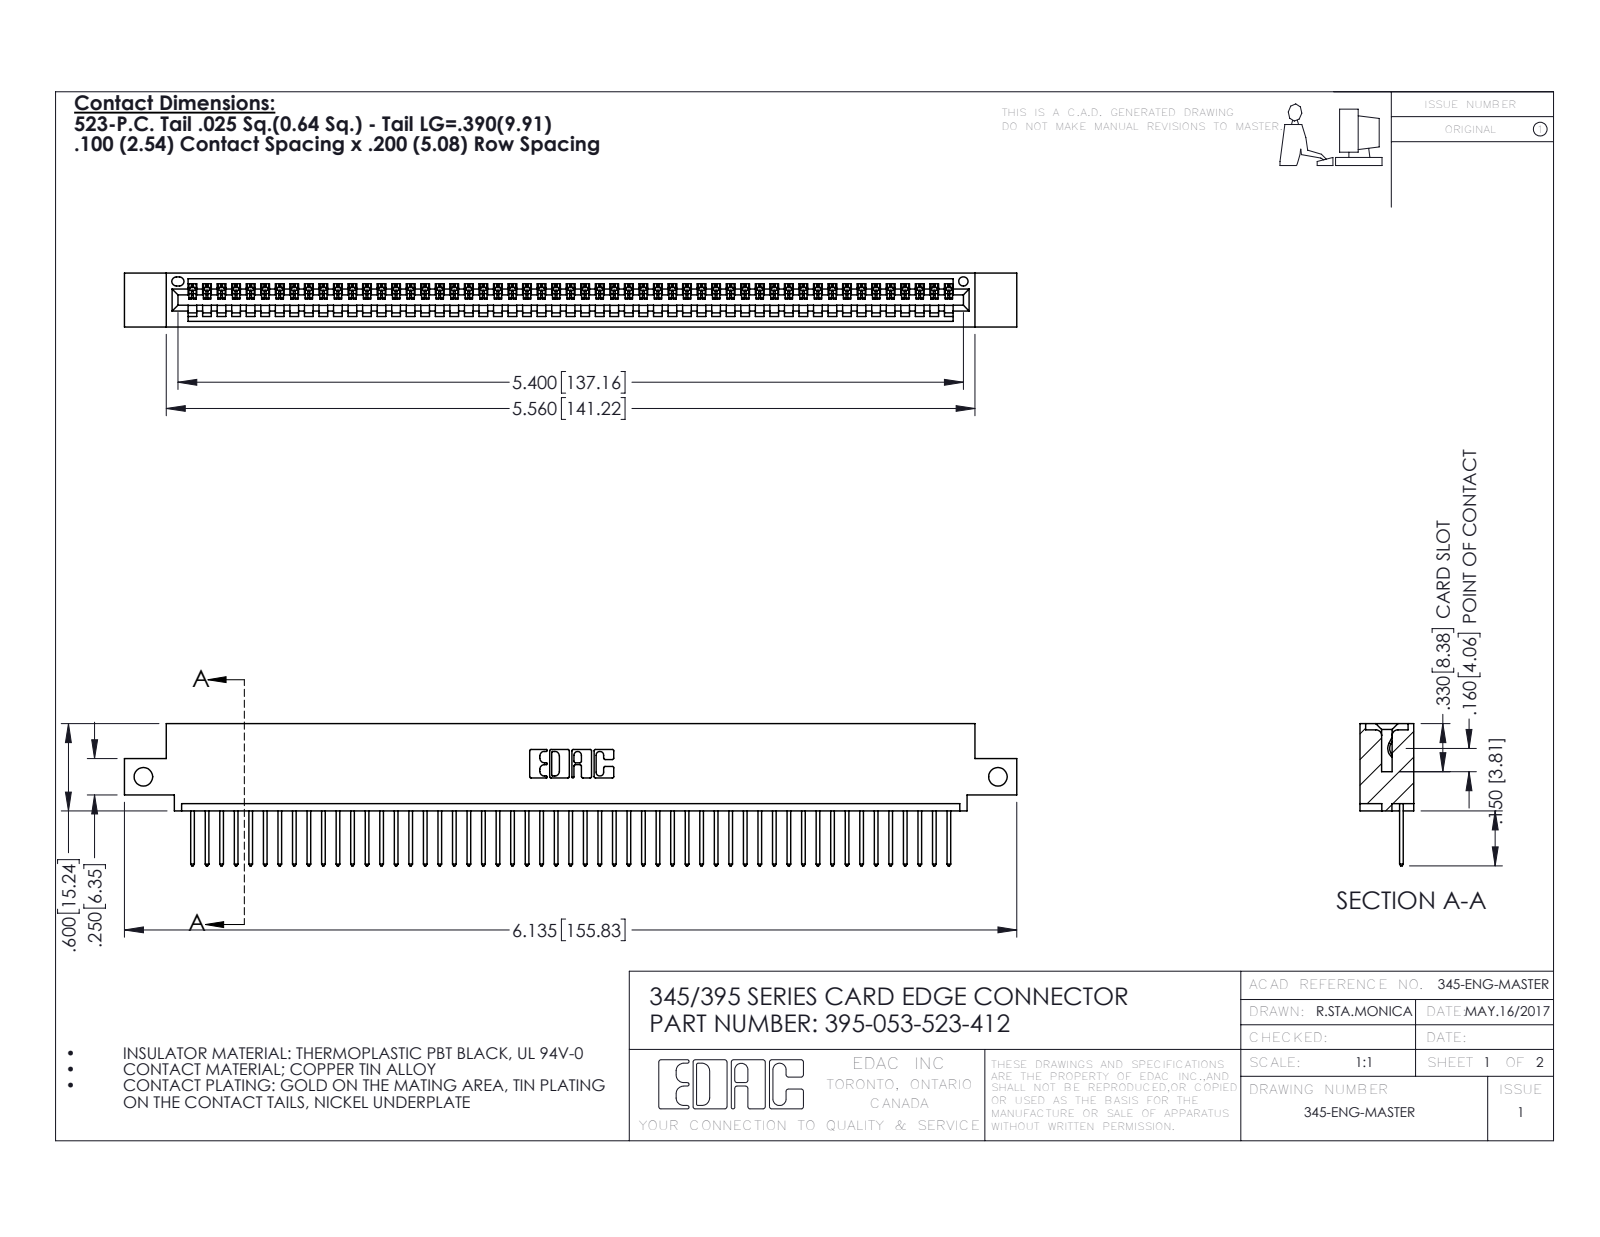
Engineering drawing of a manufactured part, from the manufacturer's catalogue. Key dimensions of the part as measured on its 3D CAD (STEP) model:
Part name (STEP PRODUCT): 345 Part_0.110 Offset - Side Mount; 395-053-523-412; 345-292-001_345-293-123
STEP written by: SolidWorks 2016 (CONFIG_CONTROL_DESIGN)
Units: inches
Bodies: 54 solids, 3204 faces (2204 planar, 1000 cylindrical, 0 other)
Overall size (bounding box): 6.135 × 0.977 × 0.37
Volume: 0.898 in³ · Surface area: 30.53 in²
Round holes (diameter × count): ⌀0.128 ×2, ⌀0.064 ×1
Partial cylindrical surfaces — rounded edges, fillets, slot ends (radius × count): R0.006 ×106, R0.01 ×106, R0.01 ×22, R0.007 ×6, R0.031 ×6, R0.026 ×3, R0.031 ×2, R0.04 ×2
Main face-to-face distances: 0.298, 0.072, 0.37, 0.098, 0.272, 0.025, 0.2, 0.225, 0.149, 0.072
Hole centre spacings: 5.875
